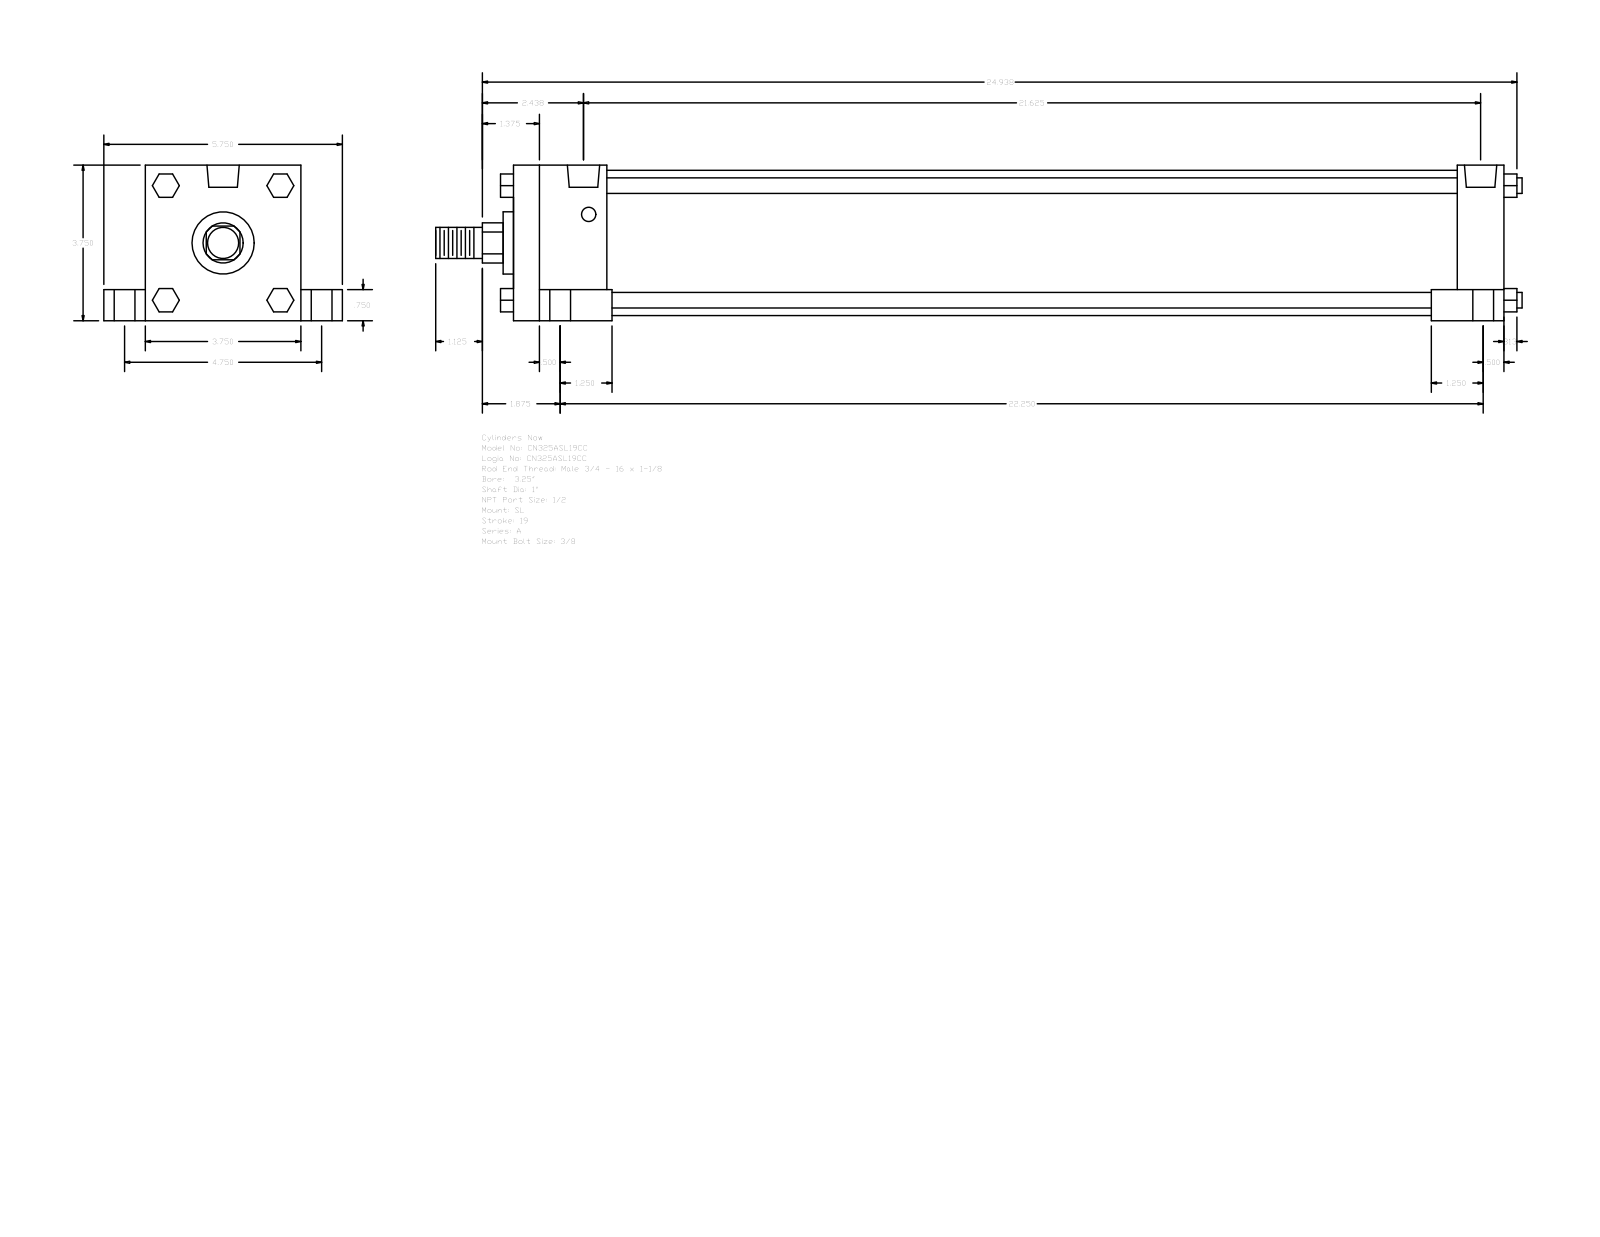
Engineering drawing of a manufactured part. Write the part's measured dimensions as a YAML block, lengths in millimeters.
part_name: "A_SL__0325_1"
step_written_by: "GSSL Pune (CONFIG_CONTROL_DESIGN)"
units: millimeters
bodies: {solids: 0, faces: 150, planar: 114, cylindrical: 36, other: 0}
overall_size: [665.16, 146.05, 95.25]
round_holes:
  - {diameter: 8.73, count: 4}
  - {diameter: 12.7, count: 4}
  - {diameter: 19.05, count: 4}
  - {diameter: 19.77, count: 2}
round_bosses_or_shafts:
  - {diameter: 9.53, count: 4}
  - {diameter: 88.9, count: 1}
  - {diameter: 38.1, count: 1}
  - {diameter: 25.4, count: 1}
  - {diameter: 19.05, count: 1}
partial_cylinders:
  - {radius: 12.29, count: 1}
face_to_face_distances: [95.24, 606.43, 19.05, 25.41, 120.65, 76.19, 57.15, 577.85, 520.7, 549.28]
hole_center_spacings: [3.18, 60.35, 60.52, 62, 62.81, 120.66, 542.92, 546.1]
